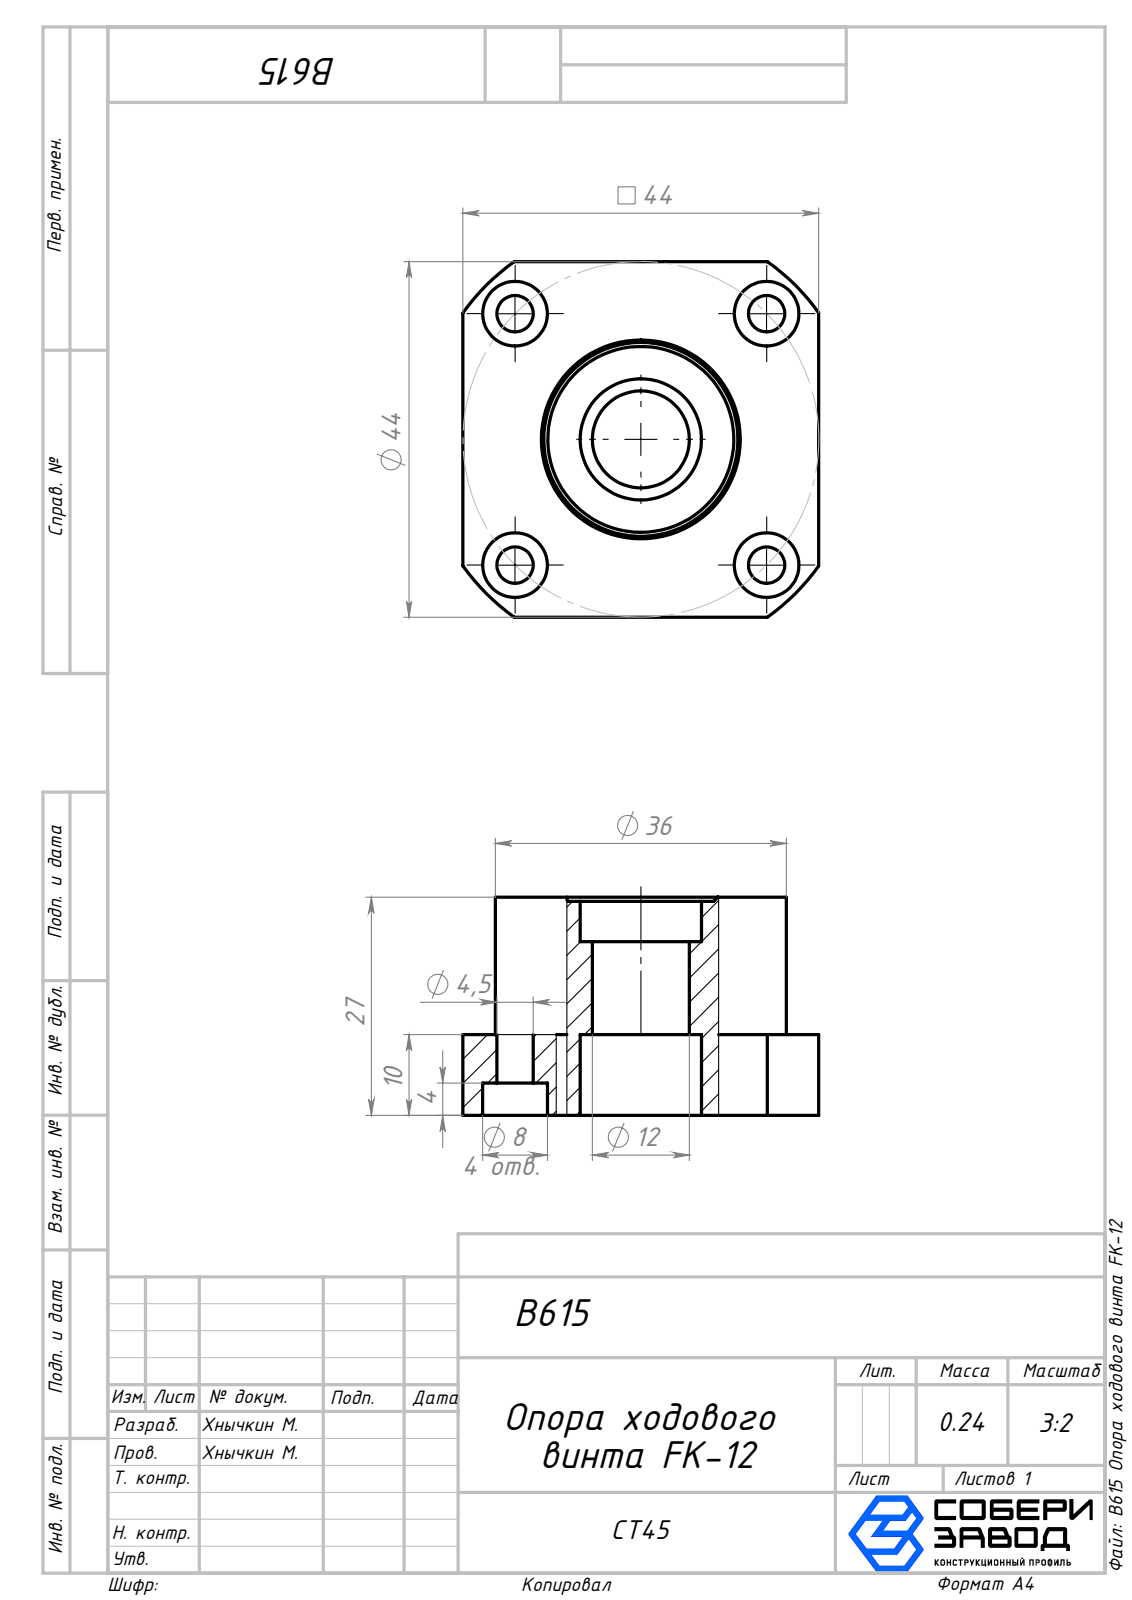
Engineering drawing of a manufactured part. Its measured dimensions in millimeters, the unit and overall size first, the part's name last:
Units: millimetres
Overall size (bounding box): 44 × 44 × 27
Round holes (diameter × count): ⌀4.5 ×4, ⌀8 ×4, ⌀12 ×1, ⌀15 ×1, ⌀24 ×1
Round bosses / shafts (diameter × count): ⌀36 ×1, ⌀23 ×1
Partial cylindrical surfaces — rounded edges, fillets, slot ends (radius × count): R27 ×1
Main face-to-face distances: 10, 27, 17, 44, 3, 7, 24, 26.5, 23.5, 16.5
Hole centre spacings: 22.01, 31.12, 44.01
Volume: 30 774 mm³ · Surface area: 8 895 mm²
Bodies: 1 solid, 52 faces (16 planar, 32 cylindrical, 4 other)
Part name (STEP PRODUCT): B615 Опора ходового винта FK-12
STEP written by: SolidWorks 2026 (AUTOMOTIVE_DESIGN)
